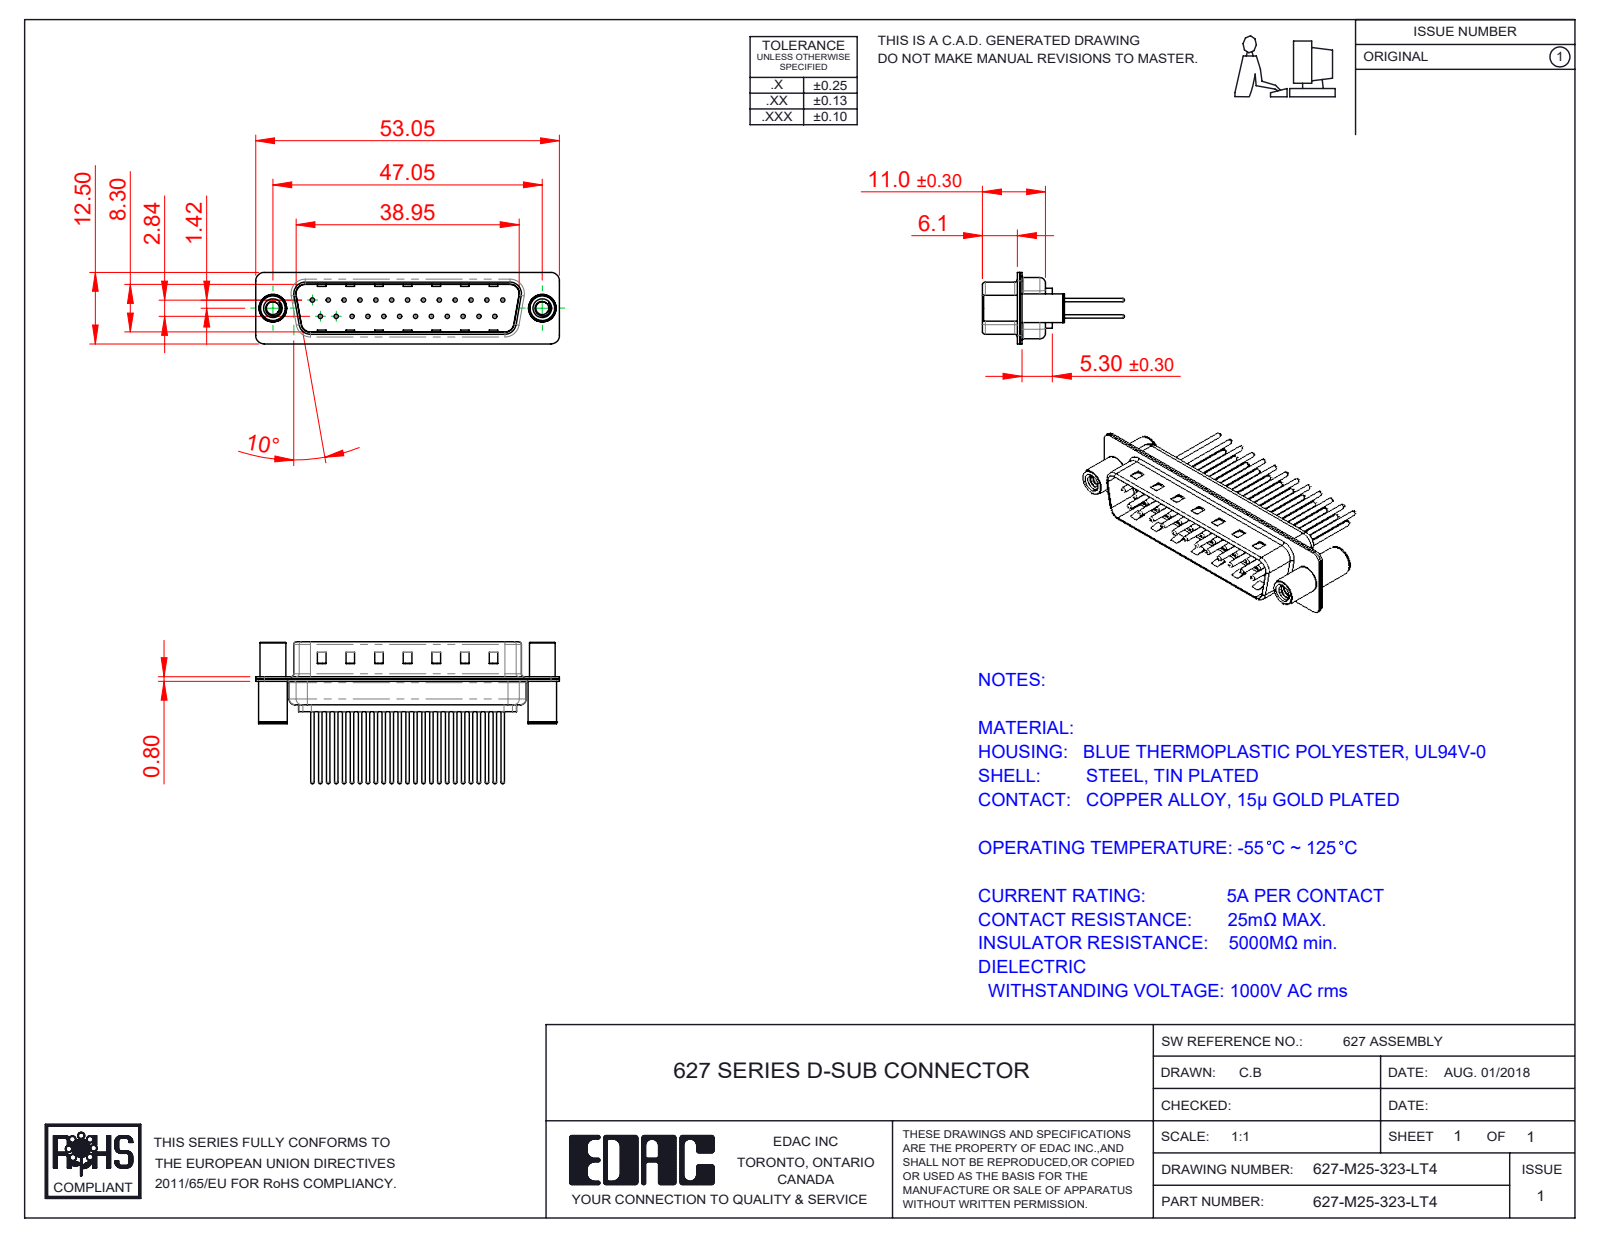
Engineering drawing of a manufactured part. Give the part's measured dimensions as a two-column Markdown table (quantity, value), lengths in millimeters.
| quantity | value |
| --- | --- |
| part name | 627M Contact Row 2_23; 627M Housing_25 Contacts; 627-M25-323-LT4; 627M Shell Front_25 Contacts (+3 more) |
| STEP written by | SolidWorks 2020 (CONFIG_CONTROL_DESIGN) |
| units | millimeters |
| bodies | 30 solids, 1387 faces (352 planar, 539 cylindrical, 496 other) |
| overall size | 53.05 × 24.77 × 12.5 |
| volume | 3 055 mm³ |
| surface area | 7 696 mm² |
| round holes (diameter × count) | 0.75 × 25, 1.6 × 25, 2 × 25, 2.26 × 2, 3.26 × 2, 4 × 2, 4.8 × 2 |
| round bosses / shafts (diameter × count) | 1.5 × 25, 0.6 × 25, 5 × 2, 4.9 × 2, 4.5 × 2 |
| partial cylindrical surfaces (radius × count) | 1.5 × 16, 2 × 12, 0.5 × 8, 1.6 × 8, 0.25 × 4, 0.6 × 4, 0.65 × 4, 0.9 × 4 |
| main face-to-face distances | 0.4, 0.8, 9.5, 9.1, 8.7, 9.9, 1.2, 5.7, 6.1, 0.75 |
| hole center spacings | 3.16, 2.77, 5.54, 8.31, 11.08, 13.85, 16.62, 5.03 |
